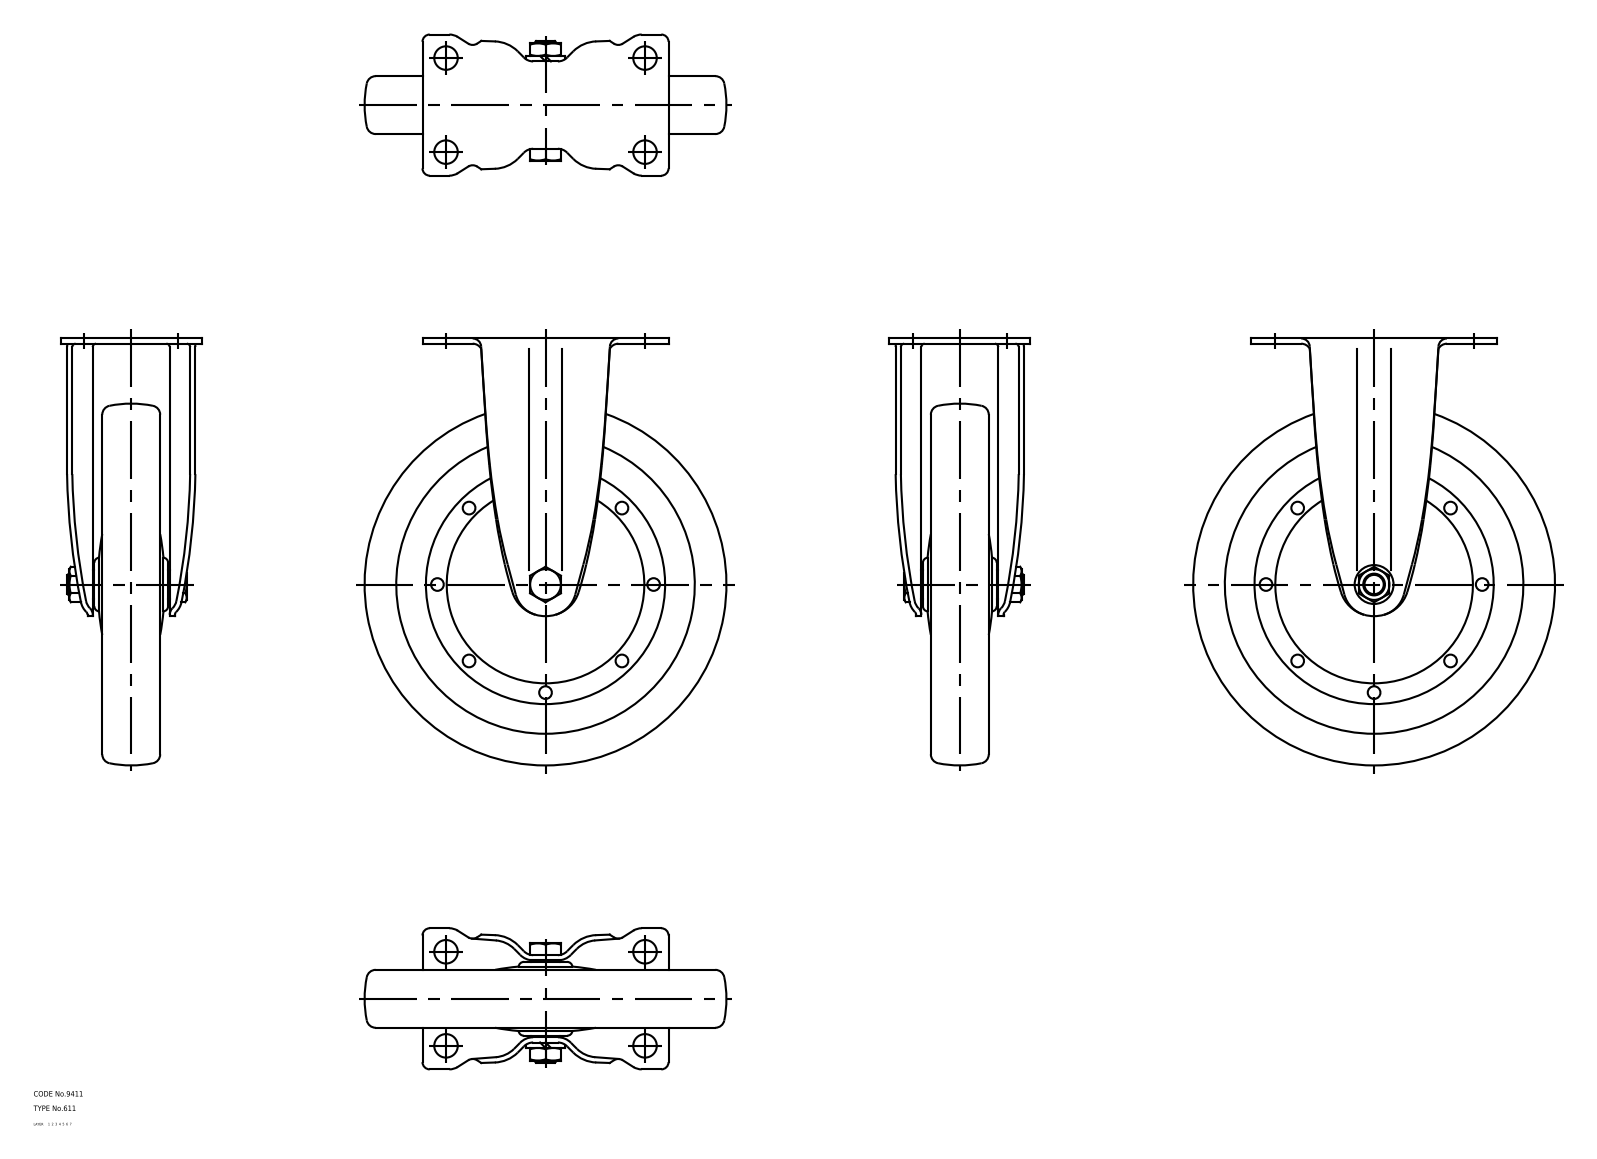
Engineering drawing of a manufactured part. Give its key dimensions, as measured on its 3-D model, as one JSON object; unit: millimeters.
{"part_name": "67125868; 67125881; 67125894", "step_written_by": "CADfix (AUTOMOTIVE_DESIGN)", "units": "millimeters", "bodies": {"solids": 3, "faces": 266, "planar": 0, "cylindrical": 0, "other": 266}, "overall_size": [236, 200, 78], "volume_mm3": 923896, "surface_area_mm2": 144794}
